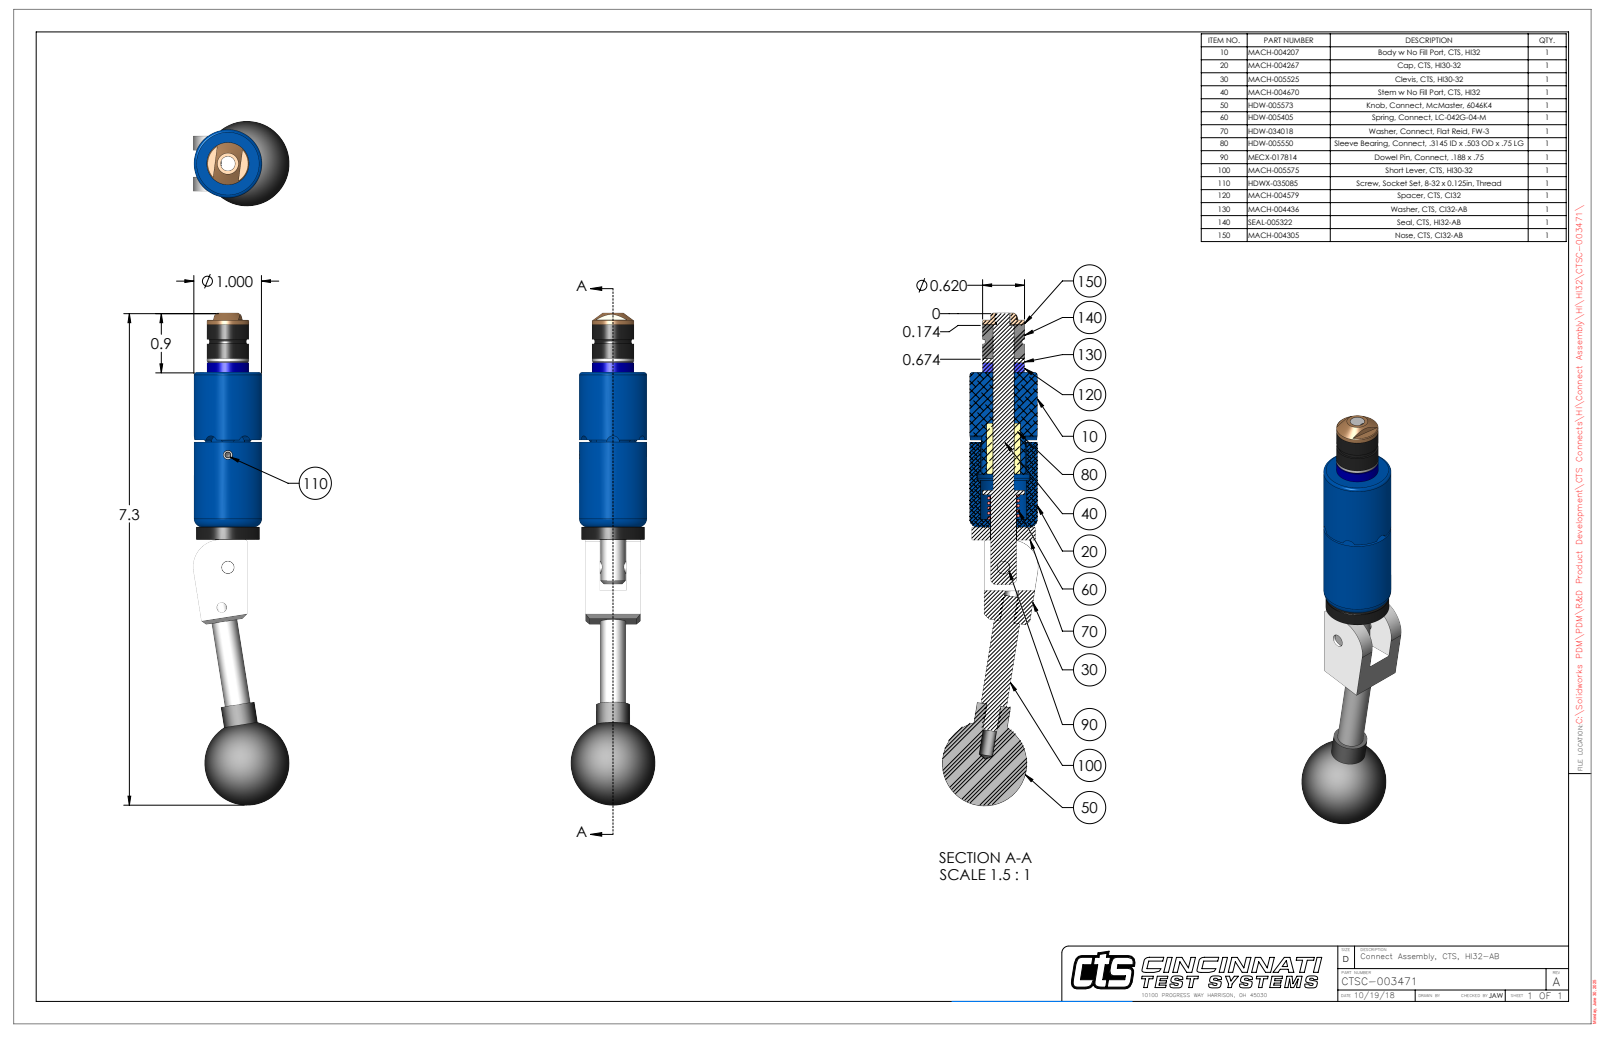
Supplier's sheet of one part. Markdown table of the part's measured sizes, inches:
| quantity | value |
| --- | --- |
| part name | CTSC-003471 |
| STEP written by | SolidWorks 2023 (AUTOMOTIVE_DESIGN) |
| units | inches |
| bodies | 10 solids, 254 faces (97 planar, 100 cylindrical, 57 other) |
| overall size | 7.268 × 1.416 × 1.25 |
| volume | 3.897 in³ |
| surface area | 32.44 in² |
| round holes (diameter × count) | 0.201 × 2, 0.136 × 1, 0.15 × 1, 0.189 × 1, 0.213 × 1, 0.31 × 1, 0.314 × 1, 0.316 × 1, 0.385 × 1, 0.392 × 1 |
| round bosses / shafts (diameter × count) | 0.25 × 2, 0.201 × 2, 1 × 1, 0.936 × 1, 0.62 × 1, 0.618 × 1, 0.5 × 1, 0.38 × 1 |
| partial cylindrical surfaces (radius × count) | 0.093 × 6, 0.029 × 2, 0.344 × 1, 0.4 × 1, 0.467 × 1 |
| main face-to-face distances | 0.21, 0.602, 2.283, 0.812, 2.47, 0.187, 0.702, 2.985, 3.172, 0.391 |
| hole center spacings | 0.599, 1.658, 2.252 |
